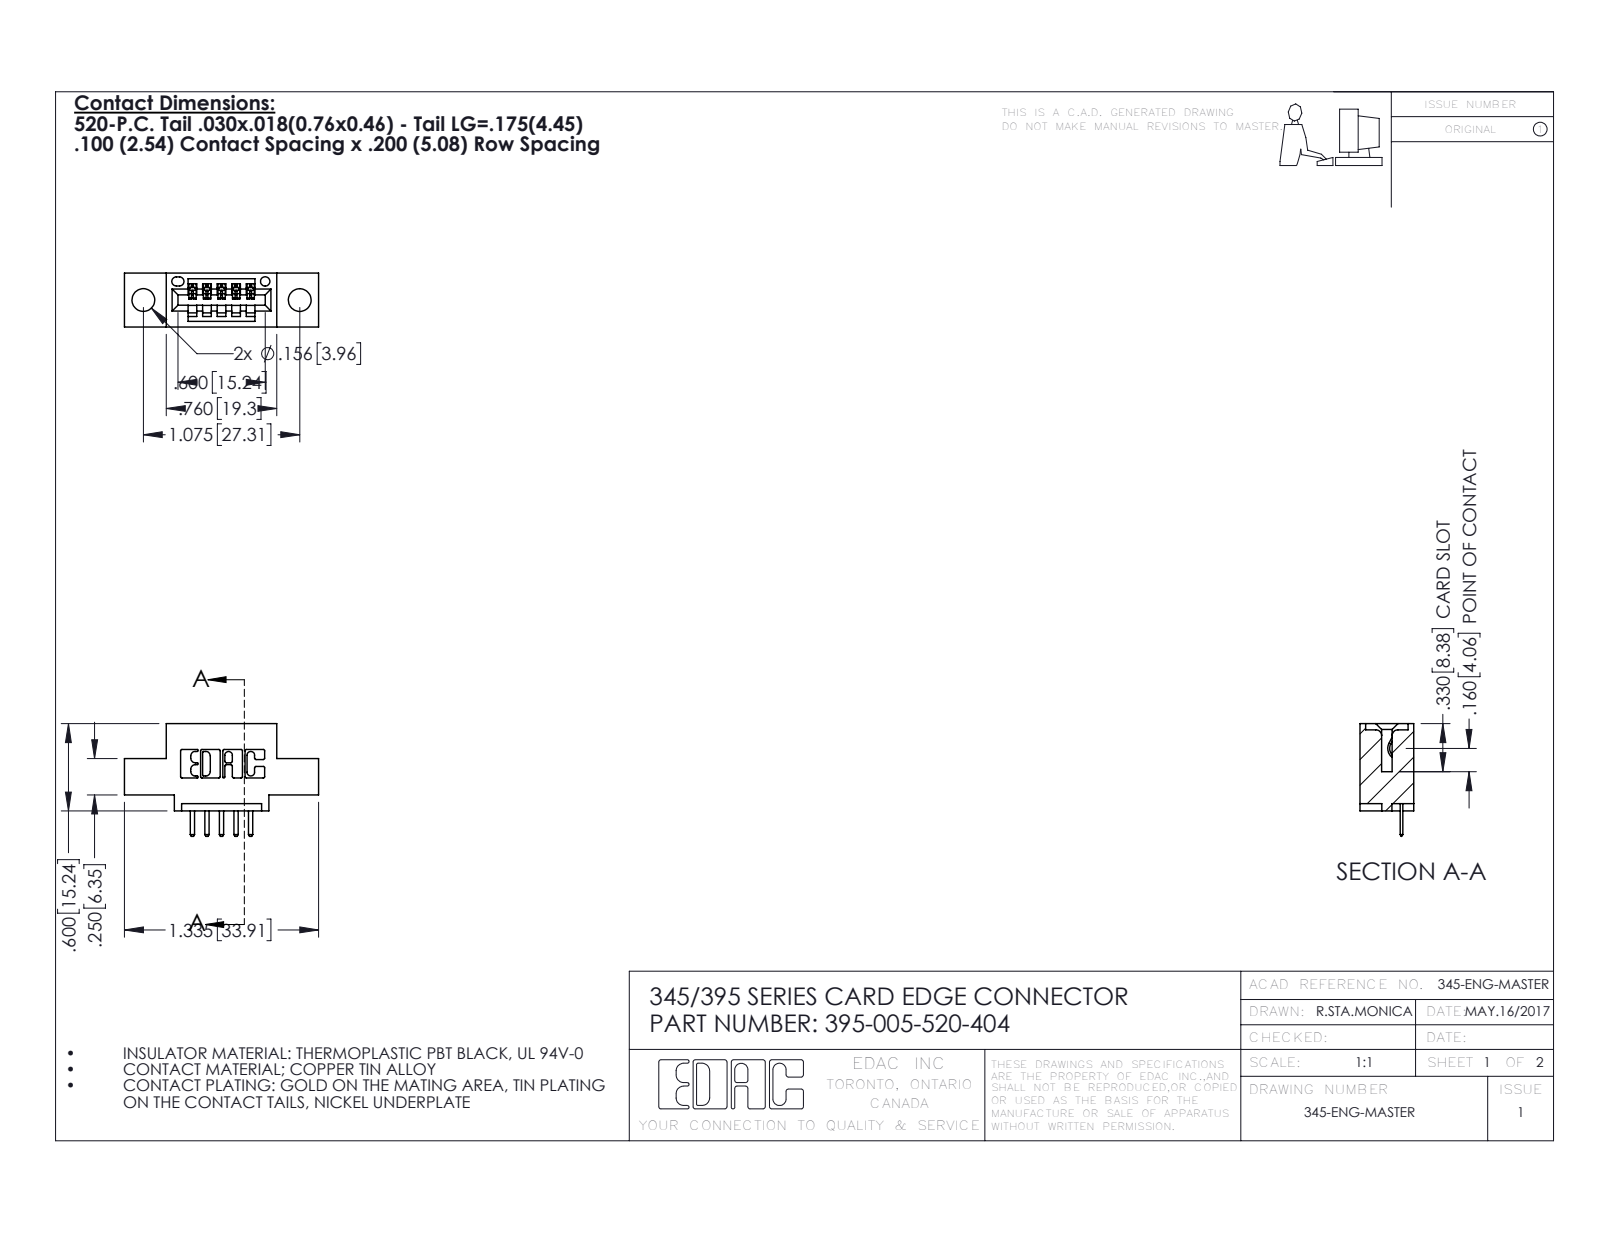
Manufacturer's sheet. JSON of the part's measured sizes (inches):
{"part_name": "345 Part_0.110 Offset - 0.156 Dia-TH; 345-292-001_345-293-120; 395-005-520-404", "step_written_by": "SolidWorks 2016 (CONFIG_CONTROL_DESIGN)", "units": "inches", "bodies": {"solids": 6, "faces": 440, "planar": 294, "cylindrical": 146, "other": 0}, "overall_size": [1.335, 0.775, 0.37], "volume_in3": 0.167, "surface_area_in2": 4.626, "round_holes": [[0.156, 2], [0.064, 1]], "partial_cylinders_radius": [[0.01, 22], [0.01, 12], [0.006, 10], [0.007, 6], [0.031, 6], [0.026, 3], [0.031, 2], [0.04, 2]], "face_to_face_distances": [0.37, 0.2, 0.1, 0.298, 0.072, 0.25, 0.025, 0.06, 0.16, 0.55], "hole_center_spacings": [0.27, 0.847, 1.075]}
